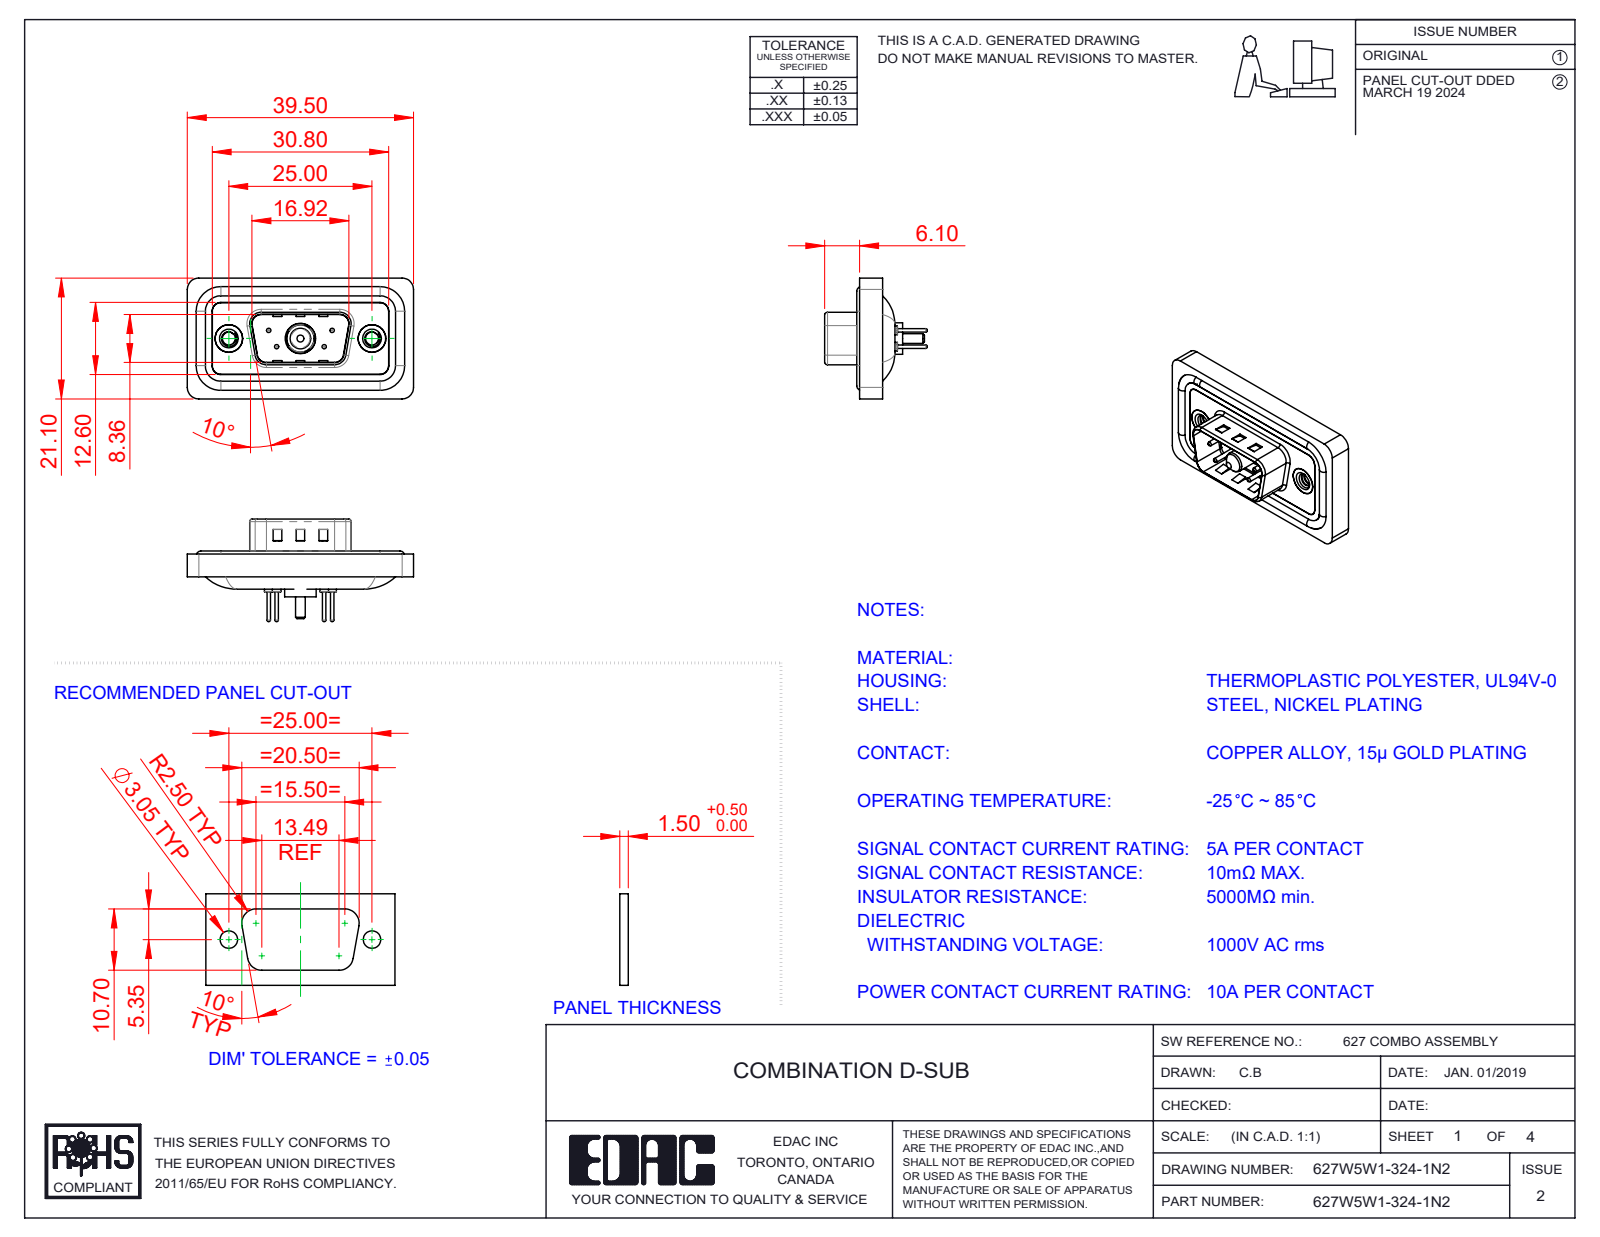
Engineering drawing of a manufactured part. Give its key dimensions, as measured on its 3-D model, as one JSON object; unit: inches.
{"part_name": "627Combo Shell Rear_09 Contacts; 627Combo Contact Row 2_24; 627W5W1-324-1N2; 627Combo Contact Row 1_24 (+5 more)", "step_written_by": "SolidWorks 2023 (CONFIG_CONTROL_DESIGN)", "units": "inches", "bodies": {"solids": 13, "faces": 598, "planar": 183, "cylindrical": 255, "other": 160}, "overall_size": [1.555, 0.831, 0.705], "volume_in3": 0.267, "surface_area_in2": 10.74, "round_holes": [[0.03, 4], [0.063, 4], [0.079, 4], [0.089, 2], [0.157, 2], [0.189, 2], [0.197, 2], [0.191, 1], [0.209, 1]], "round_bosses_or_shafts": [[0.063, 4], [0.059, 4], [0.024, 4], [0.193, 2], [0.217, 1], [0.205, 1], [0.187, 1], [0.148, 1]], "partial_cylinders_radius": [[0.059, 22], [0.079, 18], [0.02, 8], [0.063, 8], [0.01, 4], [0.024, 4], [0.026, 4], [0.035, 4]], "face_to_face_distances": [0.016, 0.043, 0.114, 0.063, 0.059, 0.122, 0.02, 0.098, 0.157, 0.031], "hole_center_spacings": [0.124, 0.225, 0.28, 0.492, 0.713, 0.173, 0.173, 0.327]}
